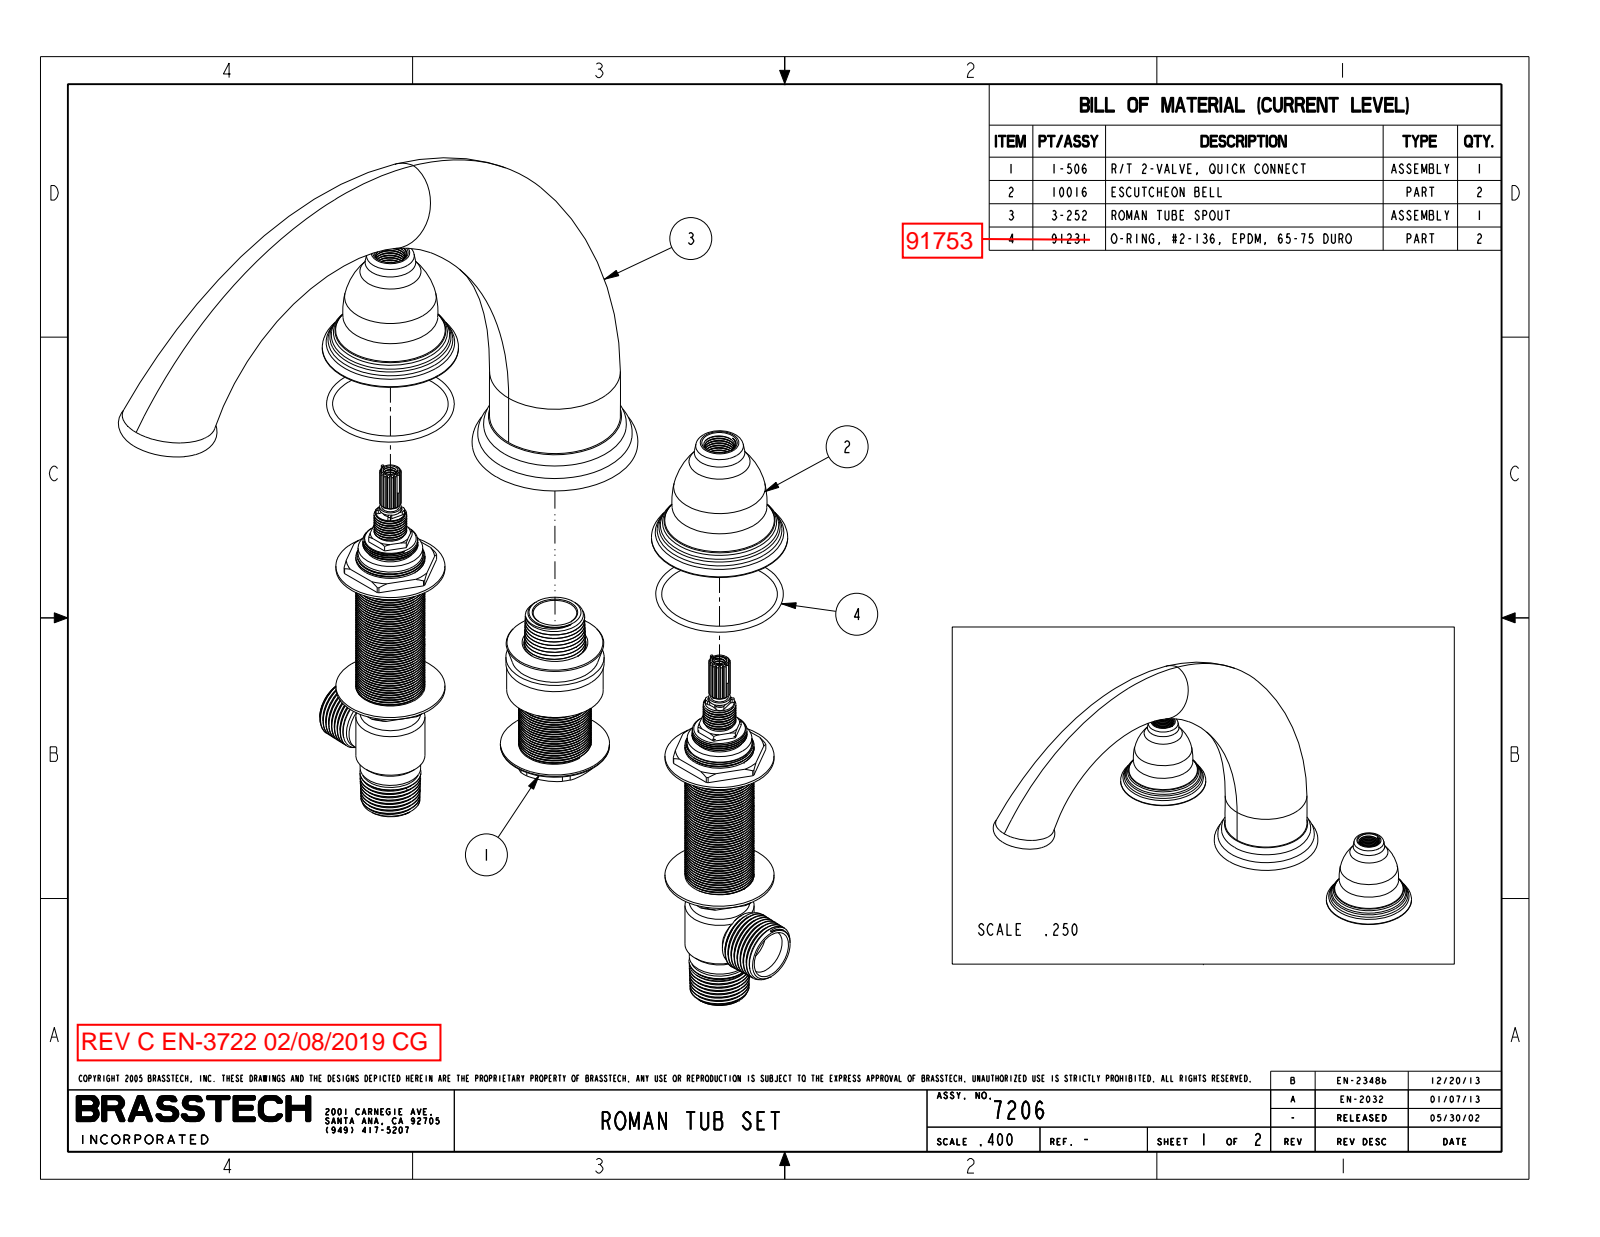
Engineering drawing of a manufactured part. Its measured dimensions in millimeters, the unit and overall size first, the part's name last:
Units: millimetres
Overall size (bounding box): 296.7 × 262.6 × 198.1
Round holes (diameter × count): ⌀5.1 ×2, ⌀6.4 ×2, ⌀12.9 ×2, ⌀15 ×2, ⌀16.9 ×2, ⌀19.1 ×2, ⌀21.1 ×2, ⌀22.4 ×2, ⌀24.5 ×2, ⌀25.4 ×2, ⌀26.4 ×2, ⌀26.5 ×2
Round bosses / shafts (diameter × count): ⌀1.1 ×4, ⌀59.4 ×2, ⌀47.6 ×2, ⌀30 ×2, ⌀28.2 ×2, ⌀26.3 ×2, ⌀24 ×2, ⌀23.9 ×2
Partial cylindrical surfaces — rounded edges, fillets, slot ends (radius × count): R1.5 ×12, R1 ×10, R2 ×8, R2.5 ×4, R1.3 ×2, R4.2 ×2, R4.8 ×2, R4.8 ×2
Main face-to-face distances: 14.1, 15.2, 19.4, 1.1, 16.7, 7.4, 17.4, 34.4, 20.3, 19.1
Hole centre spacings: 101.6, 203.2
Volume: 271 700 mm³ · Surface area: 198 200 mm²
Bodies: 6 solids, 1519 faces (368 planar, 530 cylindrical, 621 other)
Part name (STEP PRODUCT): 7206_WEB
STEP written by: PRO/ENGINEER BY PARAMETRIC TECHNOLOGY CORPORATION, 2009300 (CONFIG_CONTROL_DESIGN)
